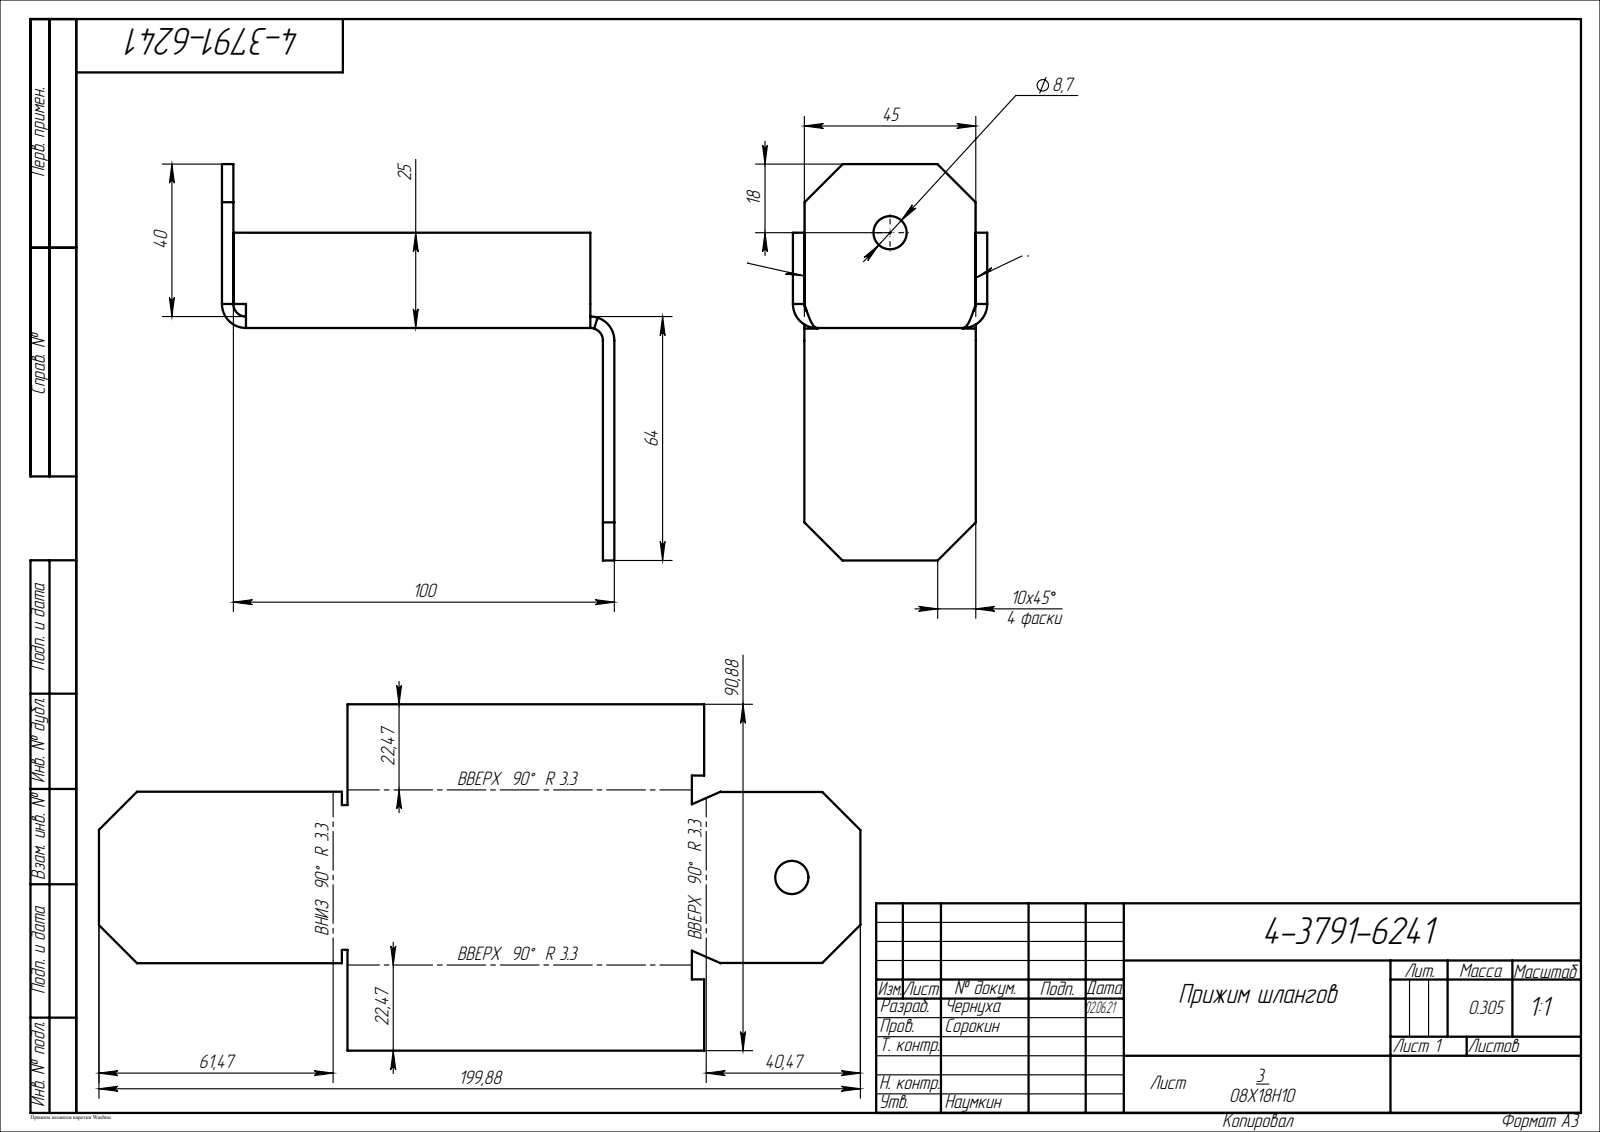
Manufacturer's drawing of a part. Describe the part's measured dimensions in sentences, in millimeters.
The part is named "4-3791-6241 Прижим шлангов". Its 3-D file was written by "SolidWorks 2021 (AUTOMOTIVE_DESIGN)". It is 1 solid with 54 faces: 42 planar, 10 cylindrical and 2 other. Overall it measures 104 by 103 by 51 millimeters. Its volume is 38 889 cubic millimeters and its surface area 27 787 square millimeters. Round holes: 1 of diameter 8.7. Partial cylindrical surfaces (rounded edges, fillets, slot ends): 4 of radius 3.3, 4 of radius 6.3. The main face-to-face distances are 3, 48, 100, 45, 51, 103, 97, 25, 22, 3.07.
